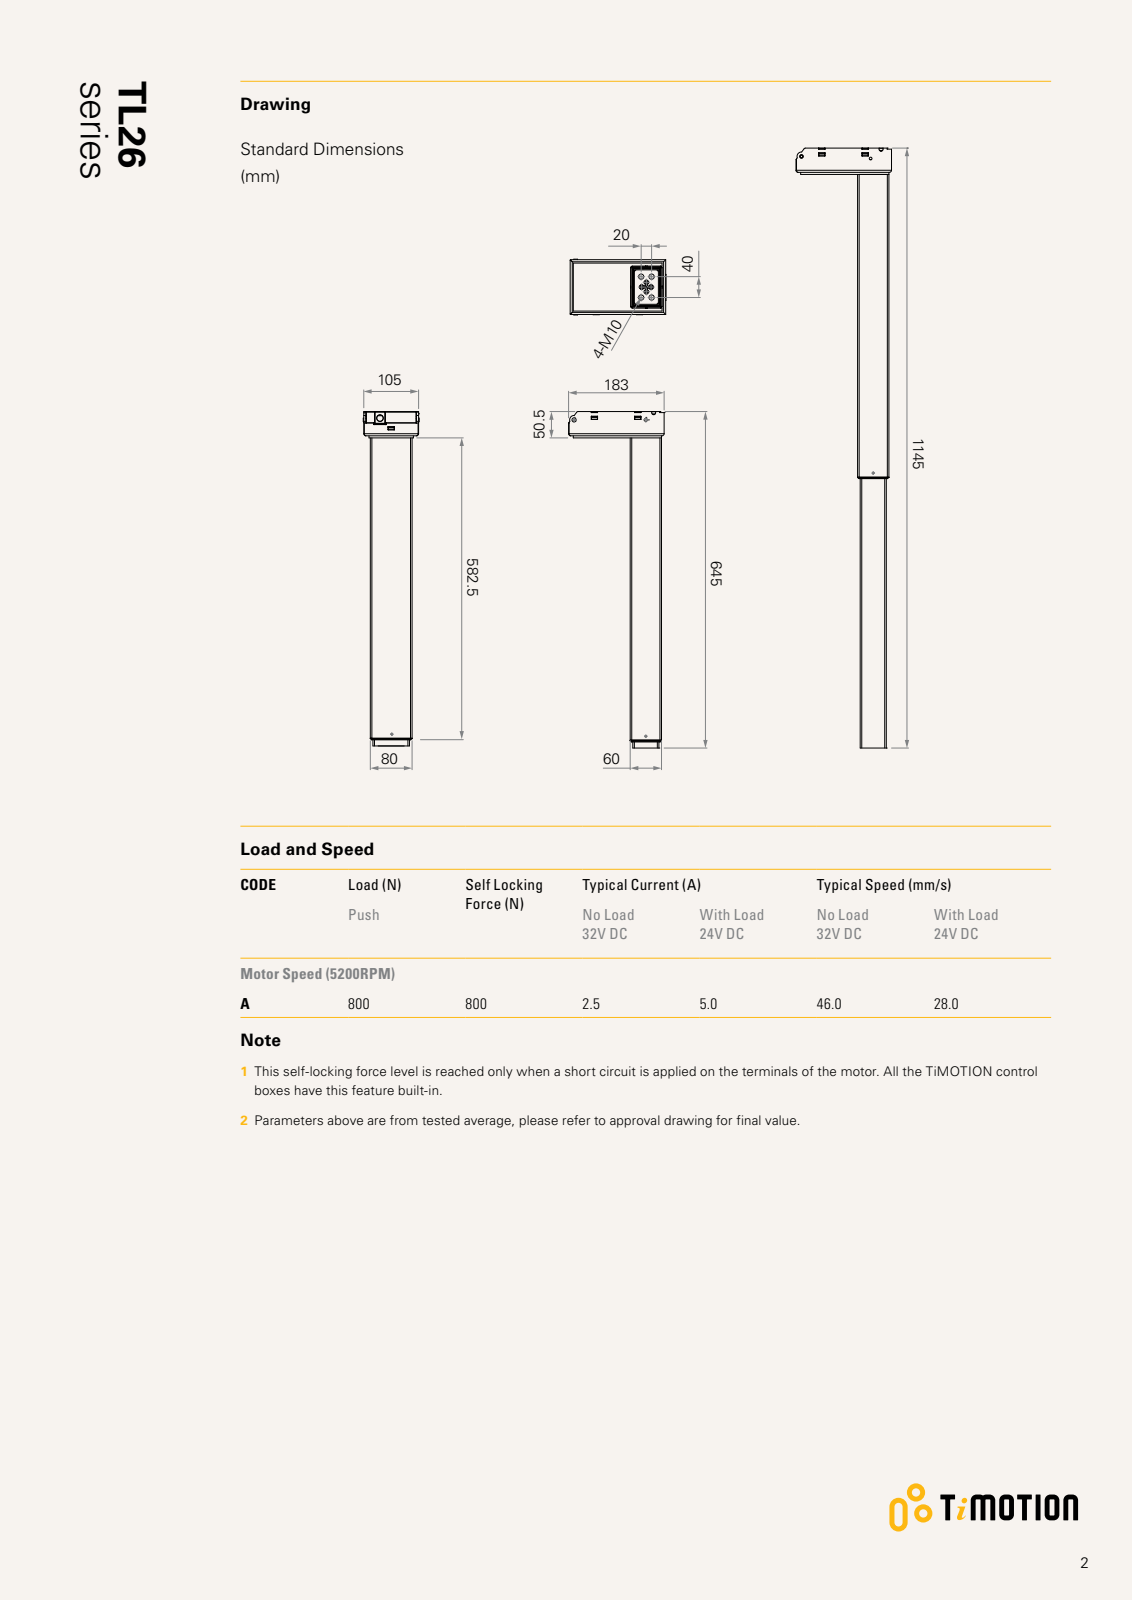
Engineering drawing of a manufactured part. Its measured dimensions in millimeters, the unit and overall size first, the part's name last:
Units: millimetres
Overall size (bounding box): 644.09 × 193.88 × 125.79
Round holes (diameter × count): ⌀5 ×10, ⌀3.2 ×6, ⌀2.5 ×4, ⌀8 ×4, ⌀2.2 ×2, ⌀4 ×2, ⌀5.2 ×2, ⌀8 ×1, ⌀10 ×1, ⌀12.2 ×1
Round bosses / shafts (diameter × count): ⌀8 ×4, ⌀5 ×4, ⌀4 ×3, ⌀8.4 ×2, ⌀7 ×2, ⌀6 ×2, ⌀2.72 ×2, ⌀13 ×1
Partial cylindrical surfaces — rounded edges, fillets, slot ends (radius × count): R0.5 ×239, R0.3 ×84, R0.2 ×64, R3 ×62, R1 ×47, R0.1 ×32, R0.75 ×16, R1.5 ×12
Main face-to-face distances: 2, 5.03, 4.97, 57.99, 52.96, 53.02, 47.99, 6.97, 7.03, 67.99
Hole centre spacings: 9, 12.73, 13, 20.02, 22.36, 27.59, 30.68, 552.55
Volume: 916 431 mm³ · Surface area: 833 628 mm²
Bodies: 17 solids, 2234 faces (832 planar, 953 cylindrical, 449 other)
Part name (STEP PRODUCT): 3D_TL26
STEP written by: SolidWorks 2015 (CONFIG_CONTROL_DESIGN)
